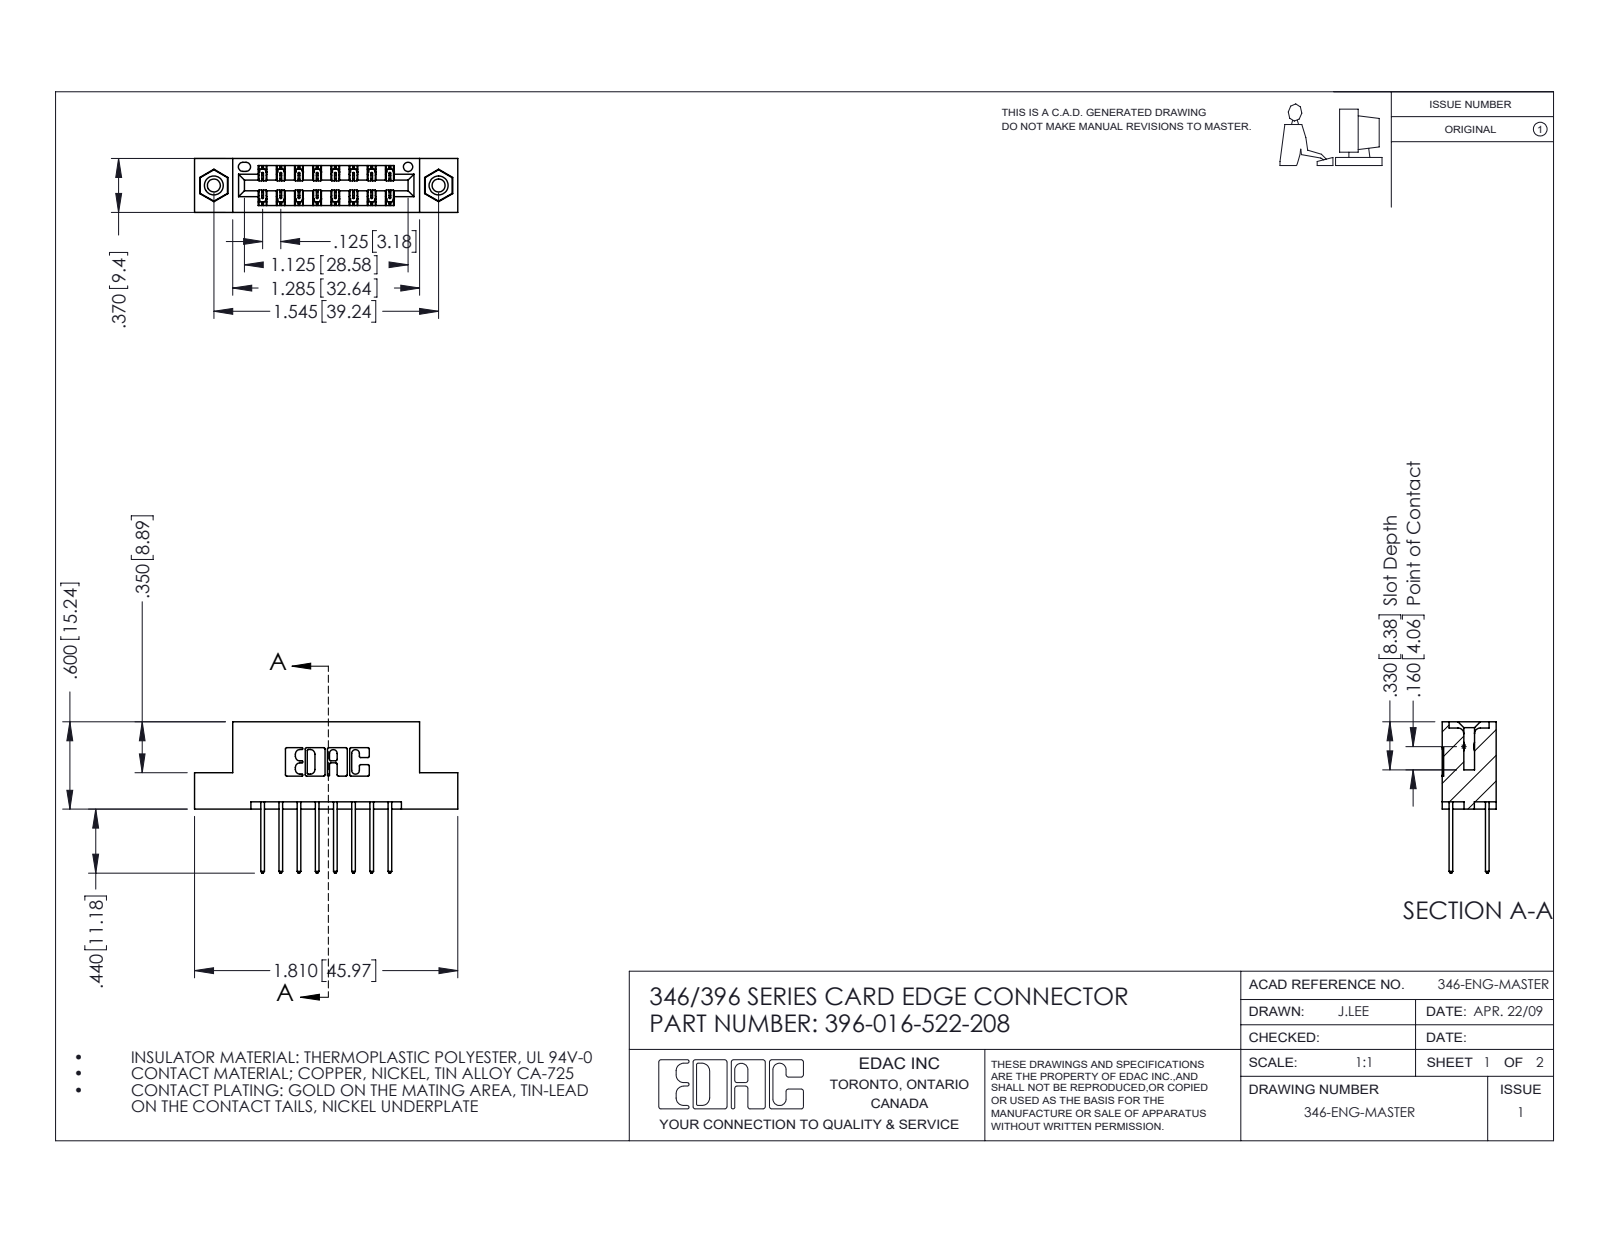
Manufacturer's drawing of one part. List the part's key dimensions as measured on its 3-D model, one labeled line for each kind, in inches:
Part name (STEP PRODUCT): 346 Part_Flush Mounting Lugs - 0.156 Dia-TI; 396-016-522-208; 345-292-001_345-293-122; 345-250-001_345-250-003-102
STEP written by: SolidWorks 2016 (CONFIG_CONTROL_DESIGN)
Units: inches
Bodies: 19 solids, 1014 faces (668 planar, 330 cylindrical, 16 other)
Overall size (bounding box): 1.81 × 1.04 × 0.37
Volume: 0.26 in³ · Surface area: 8.56 in²
Round holes (diameter × count): ⌀0.089 ×2, ⌀0.125 ×2, ⌀0.156 ×2, ⌀0.064 ×1
Round bosses / shafts (diameter × count): ⌀0.155 ×2
Partial cylindrical surfaces — rounded edges, fillets, slot ends (radius × count): R0.006 ×24, R0.01 ×22, R0.01 ×16, R0.007 ×6, R0.031 ×6, R0.026 ×3, R0.014 ×2, R0.022 ×2
Main face-to-face distances: 0.25, 0.048, 0.322, 0.37, 0.072, 0.298, 0.025, 0.275, 0.5, 0.148
Hole centre spacings: 0.246, 1.341, 1.545
